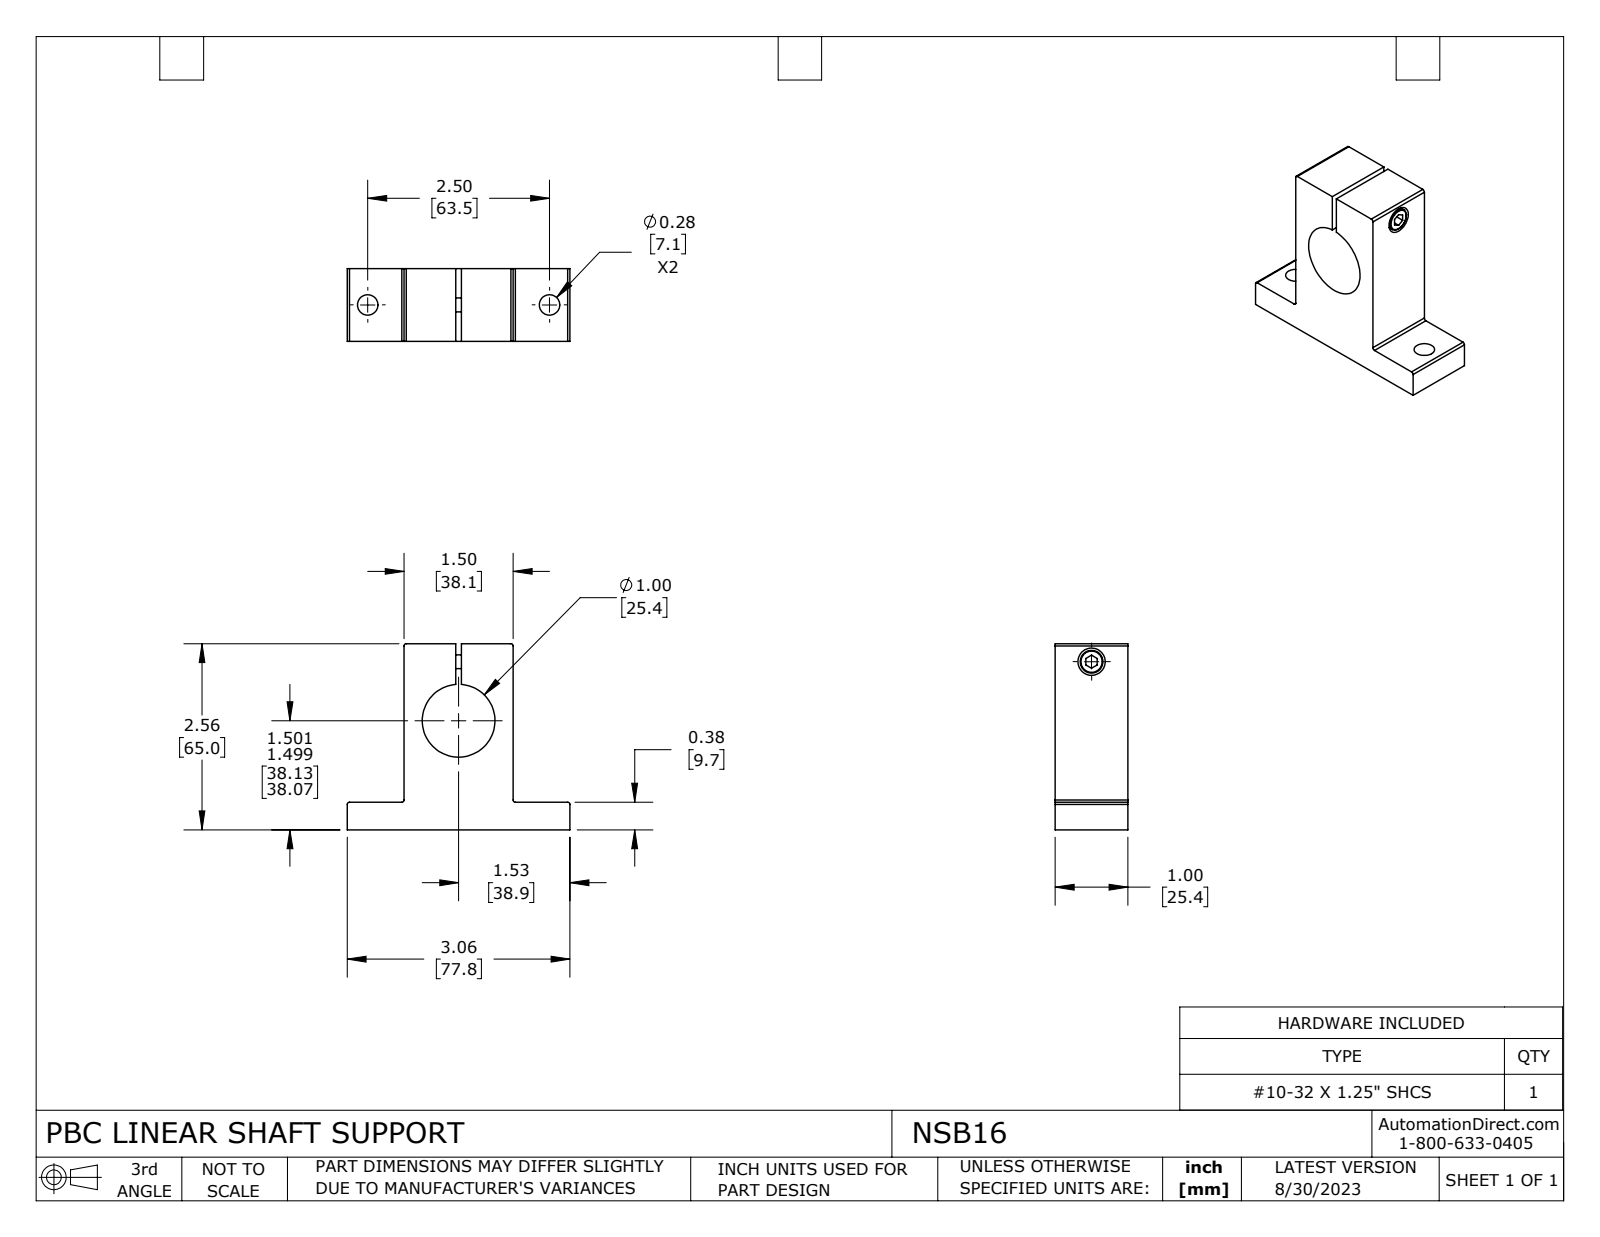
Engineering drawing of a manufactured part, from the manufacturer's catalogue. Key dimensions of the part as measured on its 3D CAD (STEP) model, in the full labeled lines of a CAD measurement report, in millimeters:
Part name (STEP PRODUCT): NSB16
STEP written by: SolidWorks 2023 (CONFIG_CONTROL_DESIGN)
Units: millimetres
Bodies: 2 solids, 51 faces (24 planar, 23 cylindrical, 4 other)
Overall size (bounding box): 77.8 × 65 × 25.4
Volume: 58 190 mm³ · Surface area: 16 030 mm²
Round holes (diameter × count): ⌀7.1 ×2, ⌀4 ×1, ⌀5.1 ×1, ⌀9.5 ×1, ⌀25.4 ×1
Round bosses / shafts (diameter × count): ⌀8 ×1, ⌀4.8 ×1
Partial cylindrical surfaces — rounded edges, fillets, slot ends (radius × count): R0.8 ×6
Main face-to-face distances: 25.4, 38.1, 65, 9.7, 55.3, 18.1, 20, 19.8, 37.9, 39.9
Hole centre spacings: 63.5
